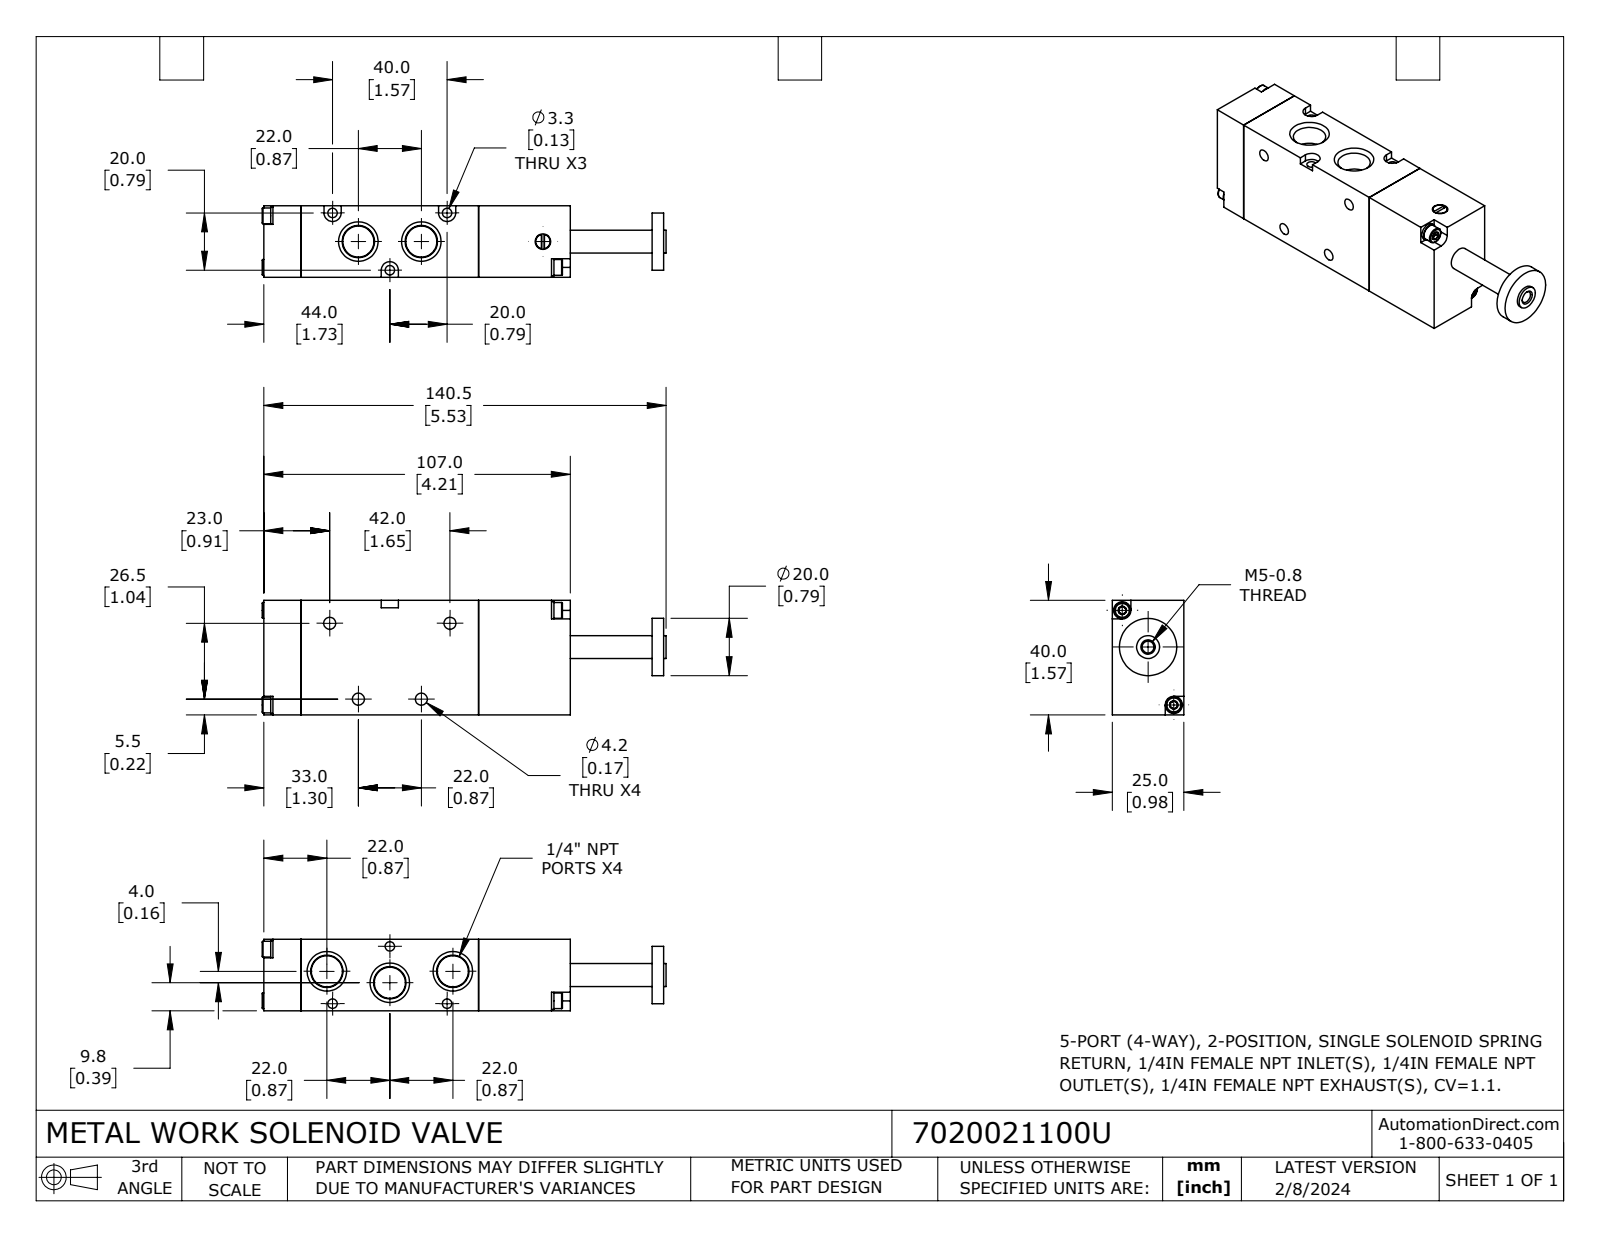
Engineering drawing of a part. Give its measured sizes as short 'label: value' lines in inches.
name: 7020021100U
written by: SolidWorks 2023 (CONFIG_CONTROL_DESIGN)
unit: in
bodies: 11 solids, 270 faces (121 planar, 71 cylindrical, 78 other)
size: 5.555 × 1.575 × 0.984
volume: 6.291 in³; area: 40.52 in²
holes: 4× ⌀0.118, 4× ⌀0.165, 3× ⌀0.13, 1× ⌀0.163, 1× ⌀0.213
bosses: 4× ⌀0.236, 4× ⌀0.217, 1× ⌀0.787, 1× ⌀0.315, 1× ⌀0.197
rounds: 3× R0.118
face distances: 0.984, 1.575, 2.441, 0.512, 2.953, 4.213, 3.701, 1.26, 0.303, 1.272
hole spacings: 0.616, 0.709, 0.87, 1.113, 1.115, 1.299, 1.48, 1.636
